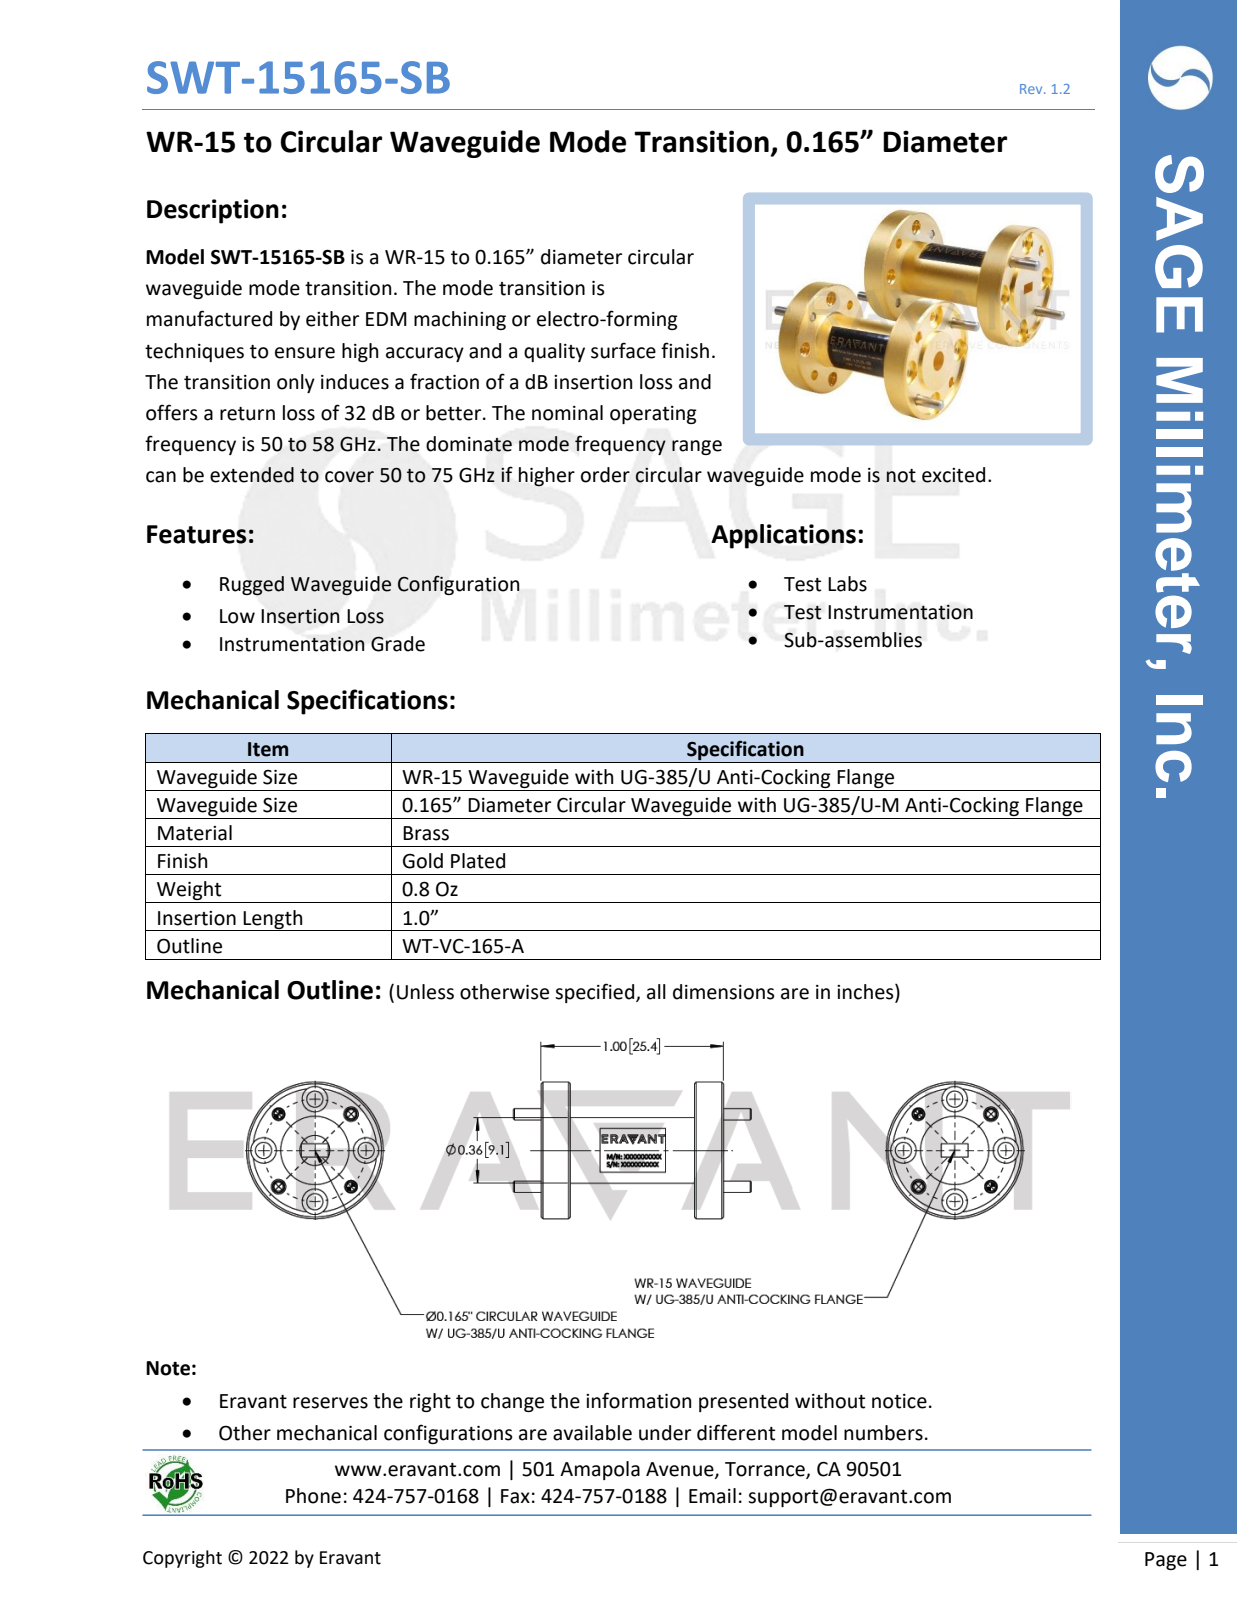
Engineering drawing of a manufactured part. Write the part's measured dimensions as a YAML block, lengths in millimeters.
part_name: "WT-VC-165-A"
step_written_by: "SolidWorks 2021 (AUTOMOTIVE_DESIGN)"
units: millimeters
bodies: {solids: 5, faces: 148, planar: 26, cylindrical: 74, other: 48}
overall_size: [33.1, 19.1, 19.1]
volume: 3110
surface_area: 2498
round_holes:
  - {diameter: 1.5, count: 4}
  - {diameter: 1.7, count: 4}
  - {diameter: 2.3, count: 4}
  - {diameter: 3.6, count: 4}
  - {diameter: 17.3, count: 1}
round_bosses_or_shafts:
  - {diameter: 1.6, count: 4}
  - {diameter: 19.1, count: 1}
  - {diameter: 9.5, count: 1}
  - {diameter: 9.5, count: 1}
  - {diameter: 9.1, count: 1}
face_to_face_distances: [24.9, 0.5, 17.3, 20.8, 3.6, 3.6, 20.8, 24.4, 21.3, 4.1]
hole_center_spacings: [5.5, 10.1, 7.1, 13.2, 14.3, 13.2, 7.1, 14.3]
